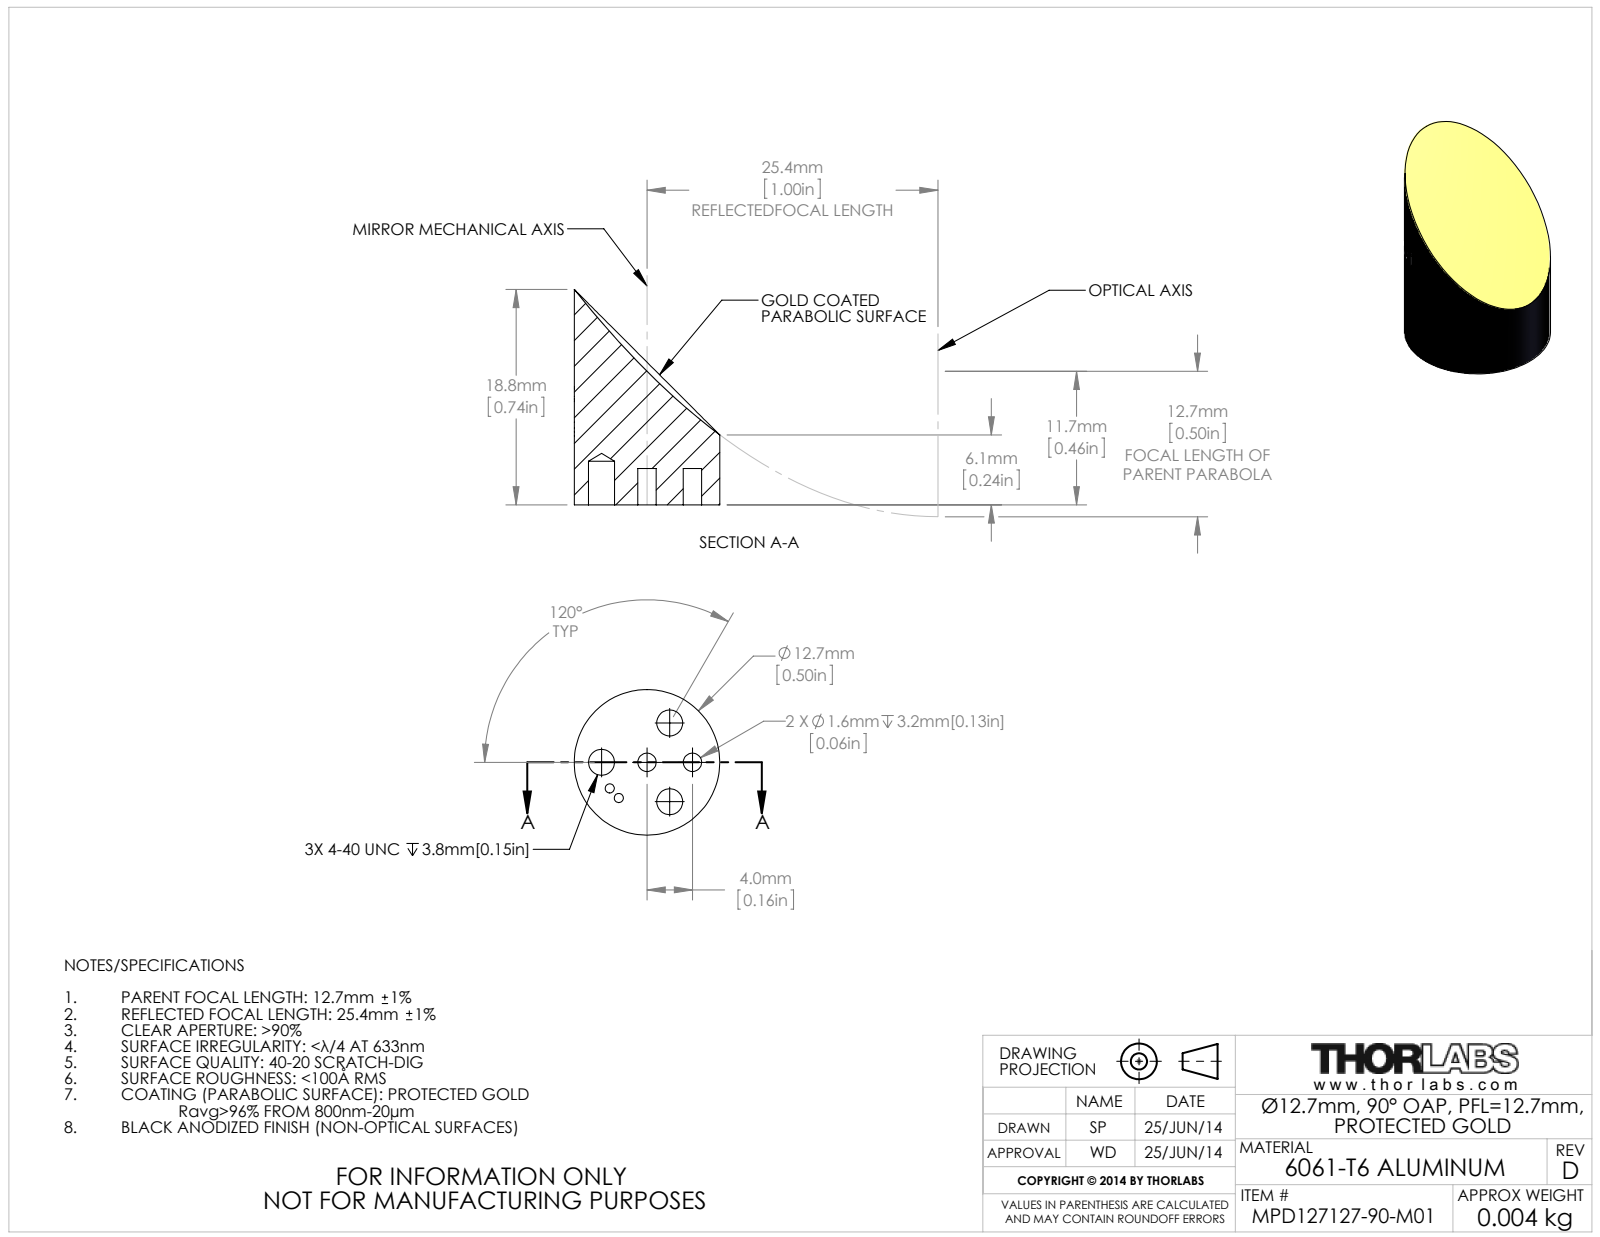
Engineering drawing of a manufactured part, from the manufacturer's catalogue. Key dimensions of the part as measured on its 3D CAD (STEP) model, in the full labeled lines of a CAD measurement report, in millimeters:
Part name (STEP PRODUCT): 21171-E0W
STEP written by: SolidWorks 2014 (CONFIG_CONTROL_DESIGN)
Units: millimetres
Bodies: 1 solid, 61 faces (3 planar, 46 cylindrical, 12 other)
Overall size (bounding box): 18.8 × 12.7 × 12.7
Volume: 1 500 mm³ · Surface area: 919 mm²
Round holes (diameter × count): ⌀2.3 ×3, ⌀1.6 ×2
Round bosses / shafts (diameter × count): ⌀12.7 ×1
Main face-to-face distances: 3.2
Hole centre spacings: 4, 6.9, 4, 8
